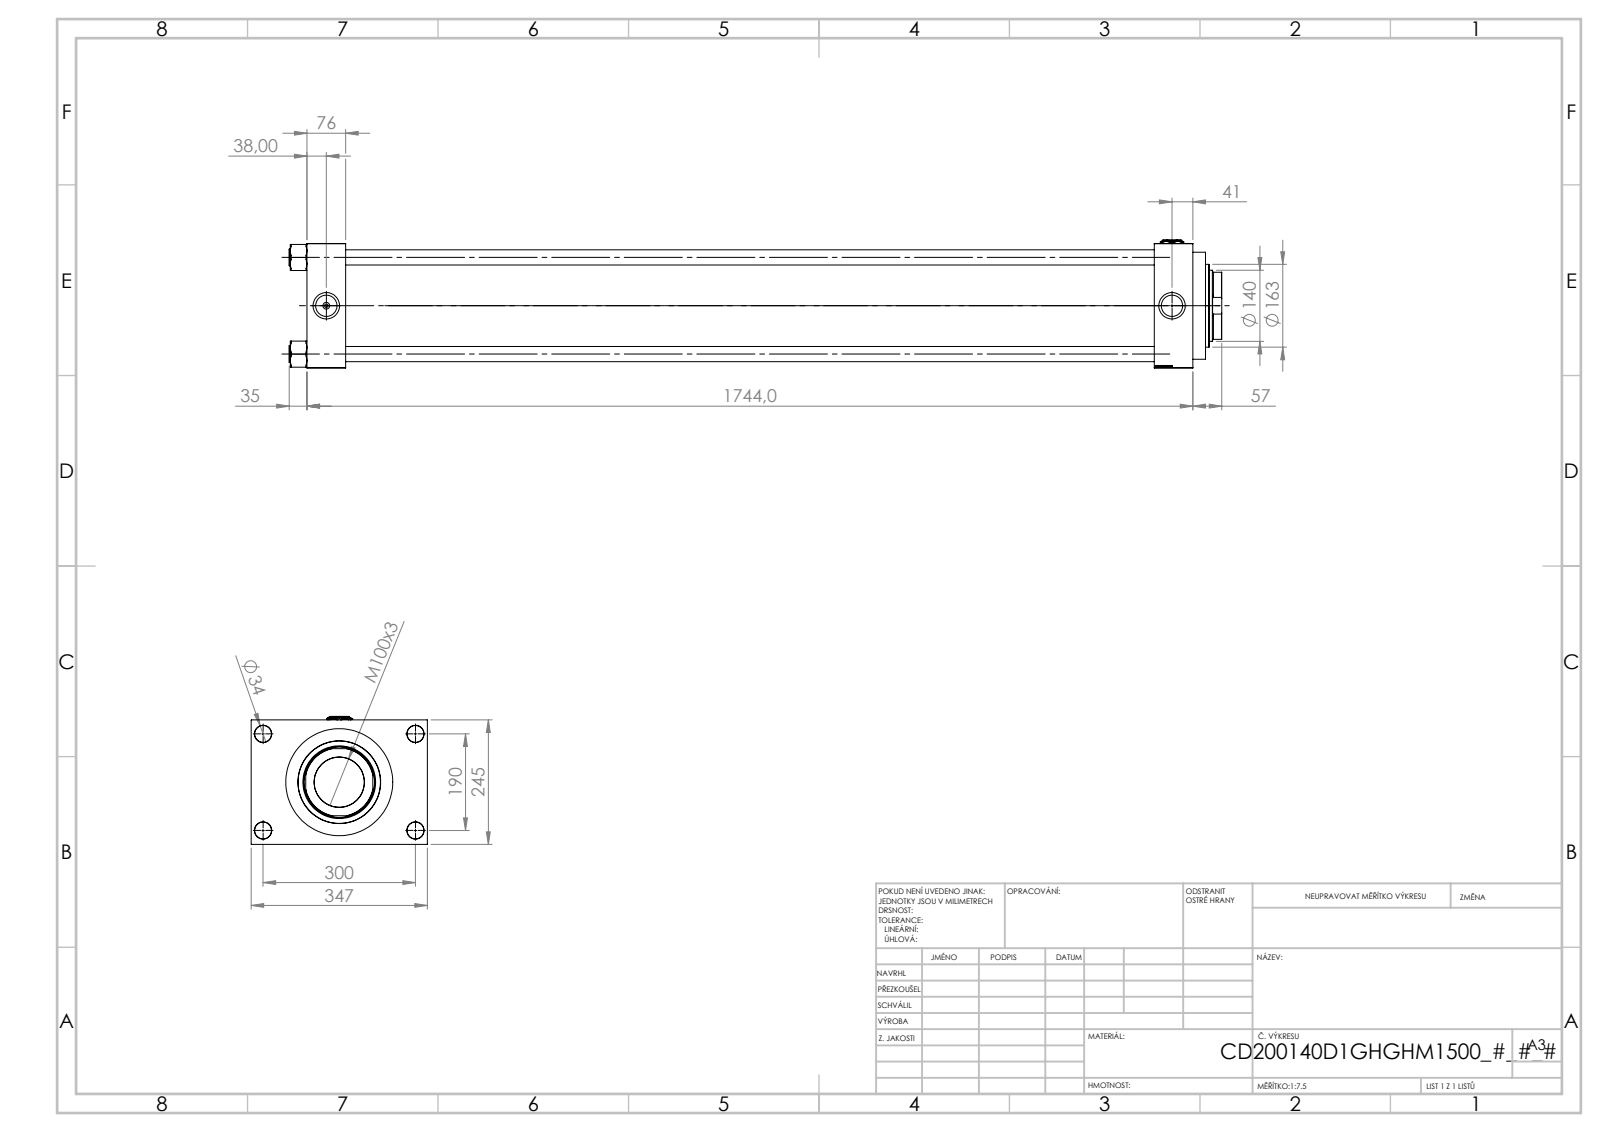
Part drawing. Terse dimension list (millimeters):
name: V215CD_VC_A; V215CD_VCP_D; Zatka_pro_OIL_PORT; V215CD_D_TYCINKA (+2 more)
written by: SolidWorks 2019 (CONFIG_CONTROL_DESIGN)
unit: mm
bodies: 12 solids, 1195 faces (567 planar, 90 cylindrical, 538 other)
size: 1836 × 347 × 252
volume: 44 710 000 mm³; area: 4 236 000 mm²
holes: 4× ⌀30, 4× ⌀33, 3× ⌀41.92, 3× ⌀52, 2× ⌀7, 1× ⌀98.5, 1× ⌀140, 1× ⌀143, 1× ⌀146, 1× ⌀200, 1× ⌀210.5
bosses: 4× ⌀33, 1× ⌀206, 1× ⌀163
rounds: 1× R68
face distances: 76, 1668, 1592, 245, 1744, 1725.74, 1649.74, 57.74, 18.26, 51
hole spacings: 54.9, 134.49, 177.55, 190.2, 197.87, 245.1, 310.18, 190
